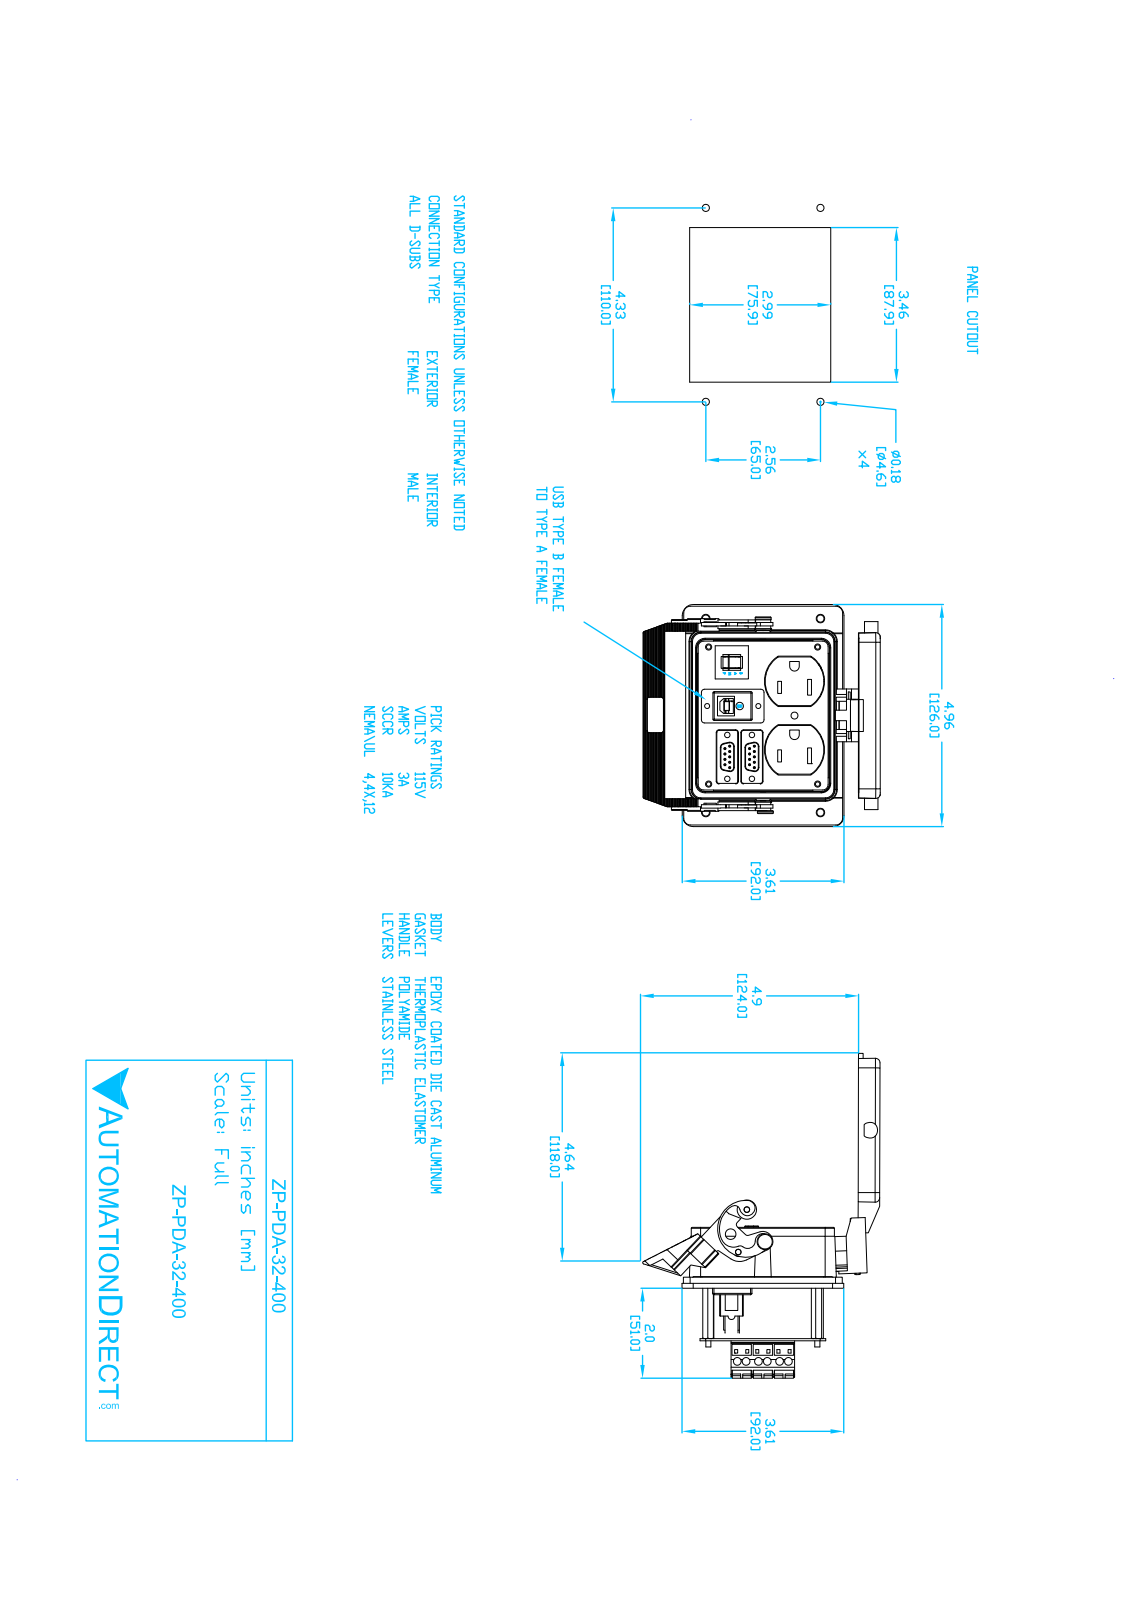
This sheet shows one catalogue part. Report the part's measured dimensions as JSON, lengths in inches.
{"part_name": "ZP-PDA-32-400", "step_written_by": "SolidWorks 2017 (AUTOMOTIVE_DESIGN)", "units": "inches", "bodies": {"solids": 1, "faces": 3954, "planar": 2383, "cylindrical": 791, "other": 780}, "overall_size": [6.857, 5.313, 4.96], "volume_in3": 13.98, "surface_area_in2": 193.6, "round_holes": [[0.045, 18], [0.144, 8], [0.098, 6], [0.173, 6], [0.09, 4], [0.122, 4], [0.134, 4], [0.16, 4], [0.19, 4], [0.091, 3], [0.097, 2], [0.12, 2]], "round_bosses_or_shafts": [[0.038, 18], [0.118, 8], [0.22, 6], [0.109, 4], [0.205, 3], [0.354, 2], [0.344, 2], [0.096, 2]], "partial_cylinders_radius": [[0.01, 22], [0.02, 22], [0.03, 19], [0.1, 18], [0.005, 17], [0.013, 12], [0.025, 12], [0.25, 12]], "face_to_face_distances": [0.135, 0.048, 1.625, 0.895, 0.847, 0.73, 1.577, 0.977, 0.247, 0.6], "hole_center_spacings": [0.12, 0.759, 0.787, 0.75, 0.125, 0.24, 0.214, 0.832]}
